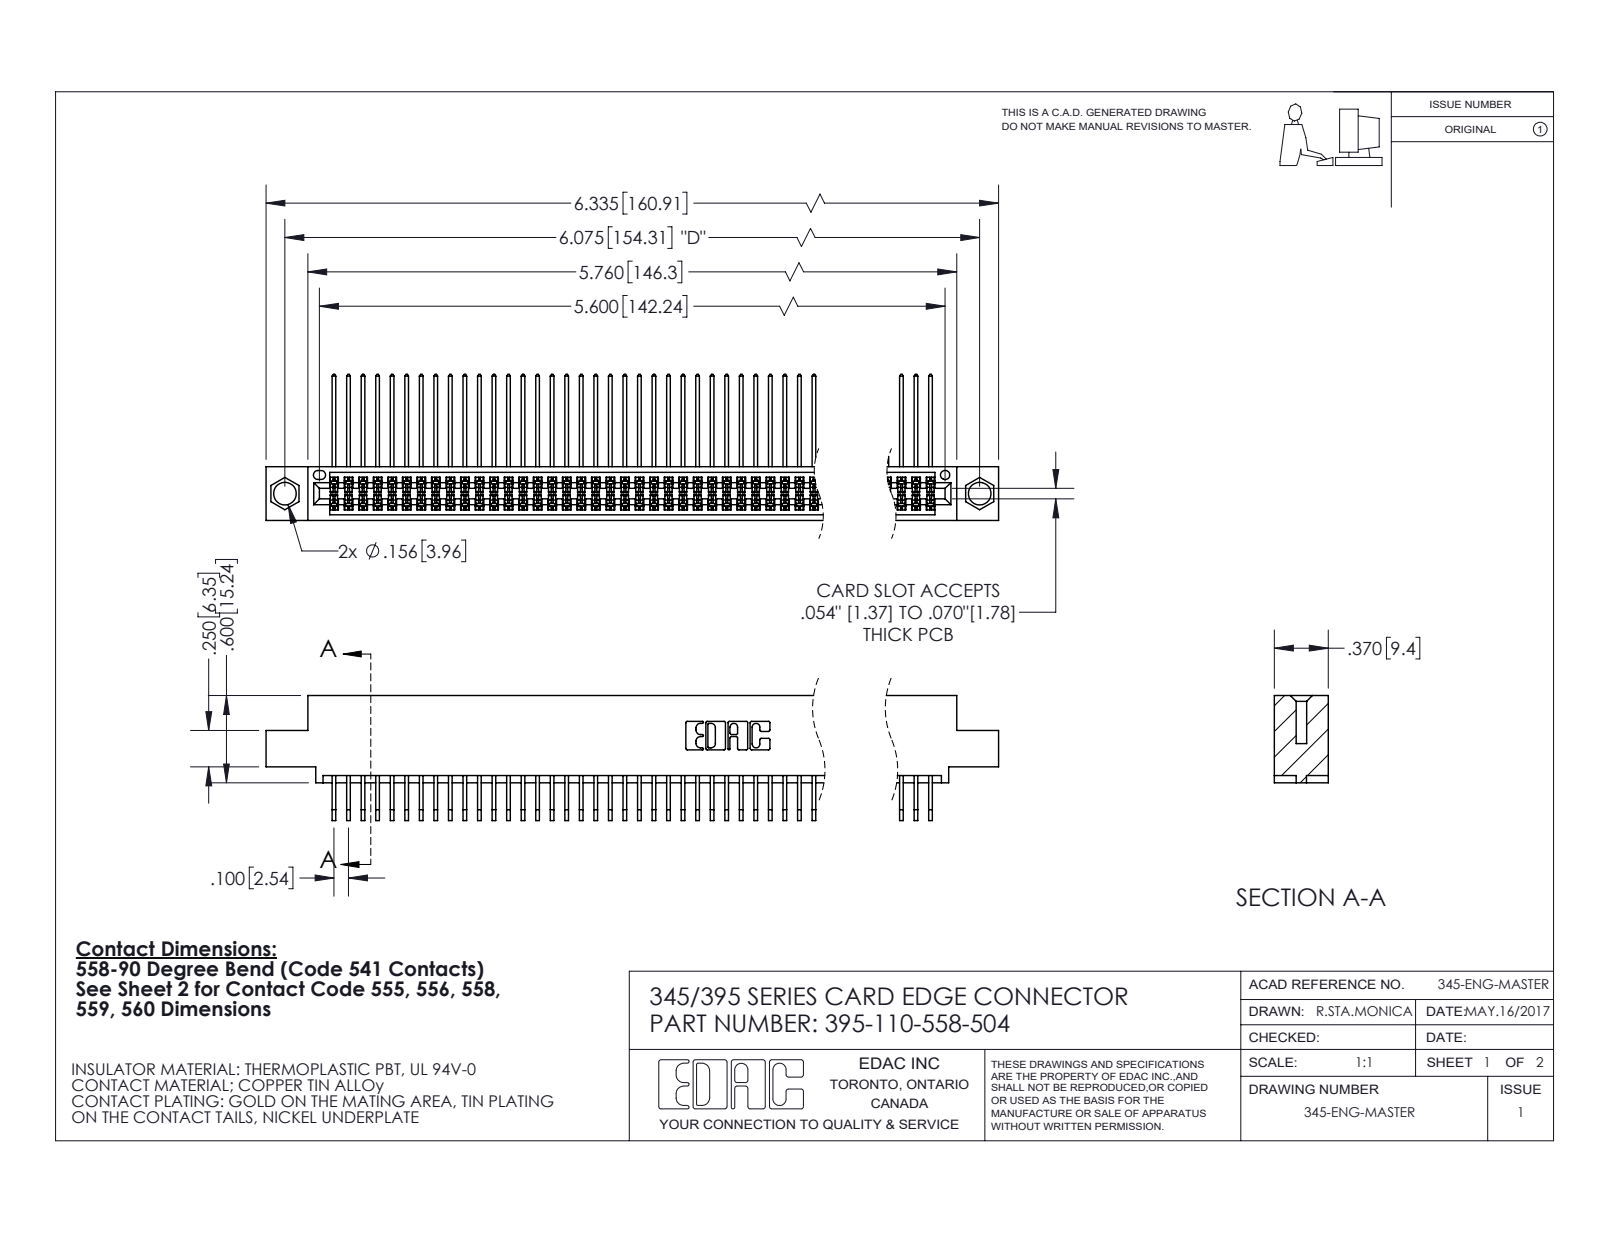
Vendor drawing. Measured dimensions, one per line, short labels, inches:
name: 345 Part_0.110 Offset - 0.156 Dia-TI; 395-110-558-504; 345-292-001_558 559 Tail - 1; 345-292-001_558 Tail - 2
written by: SolidWorks 2020 (CONFIG_CONTROL_DESIGN)
unit: in
bodies: 111 solids, 5864 faces (3948 planar, 1916 cylindrical, 0 other)
size: 6.335 × 1.005 × 0.859
volume: 0.989 in³; area: 42.06 in²
holes: 2× ⌀0.156, 1× ⌀0.064
rounds: 220× R0.006, 22× R0.01, 6× R0.007, 6× R0.031, 3× R0.026, 2× R0.014, 2× R0.019, 2× R0.022
face distances: 0.072, 0.298, 0.2, 0.37, 0.098, 0.272, 0.025, 0.225, 0.025, 0.175
hole spacings: 0.27, 5.839, 6.075
